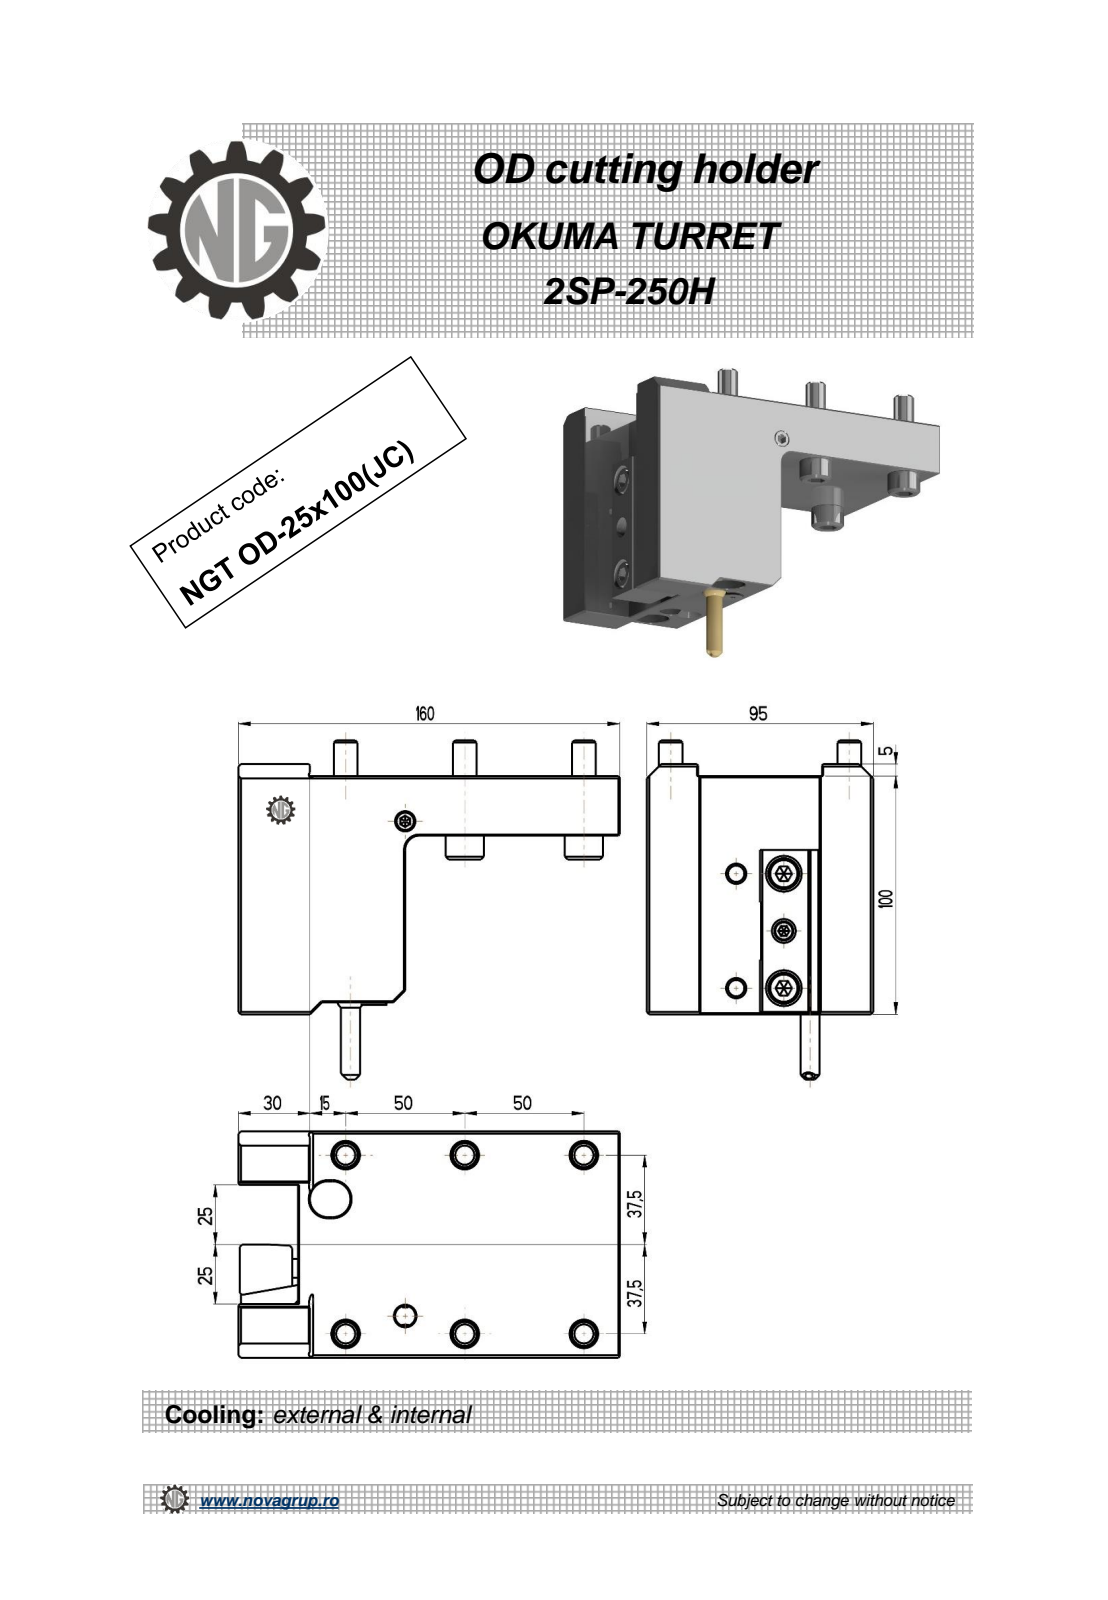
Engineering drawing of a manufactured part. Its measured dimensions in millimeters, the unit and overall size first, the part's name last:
Units: millimetres
Overall size (bounding box): 160 × 142.34 × 95
Round holes (diameter × count): ⌀3 ×1, ⌀5 ×1, ⌀8.5 ×1
Round bosses / shafts (diameter × count): ⌀10 ×6, ⌀16 ×4, ⌀8 ×4, ⌀11.2 ×1
Partial cylindrical surfaces — rounded edges, fillets, slot ends (radius × count): R0.32 ×20, R0.22 ×6, R7.5 ×2, R1 ×1, R6 ×1
Main face-to-face distances: 25, 95, 70, 45, 22.5, 72.5, 5, 100, 160, 135
Hole centre spacings: 24.7
Volume: 791 200 mm³ · Surface area: 80 461 mm²
Bodies: 1 solid, 280 faces (163 planar, 70 cylindrical, 47 other)
Part name (STEP PRODUCT): NGT_OD_25_100_JC
STEP written by: PRO/ENGINEER BY PARAMETRIC TECHNOLOGY CORPORATION, 2010280 (CONFIG_CONTROL_DESIGN)
